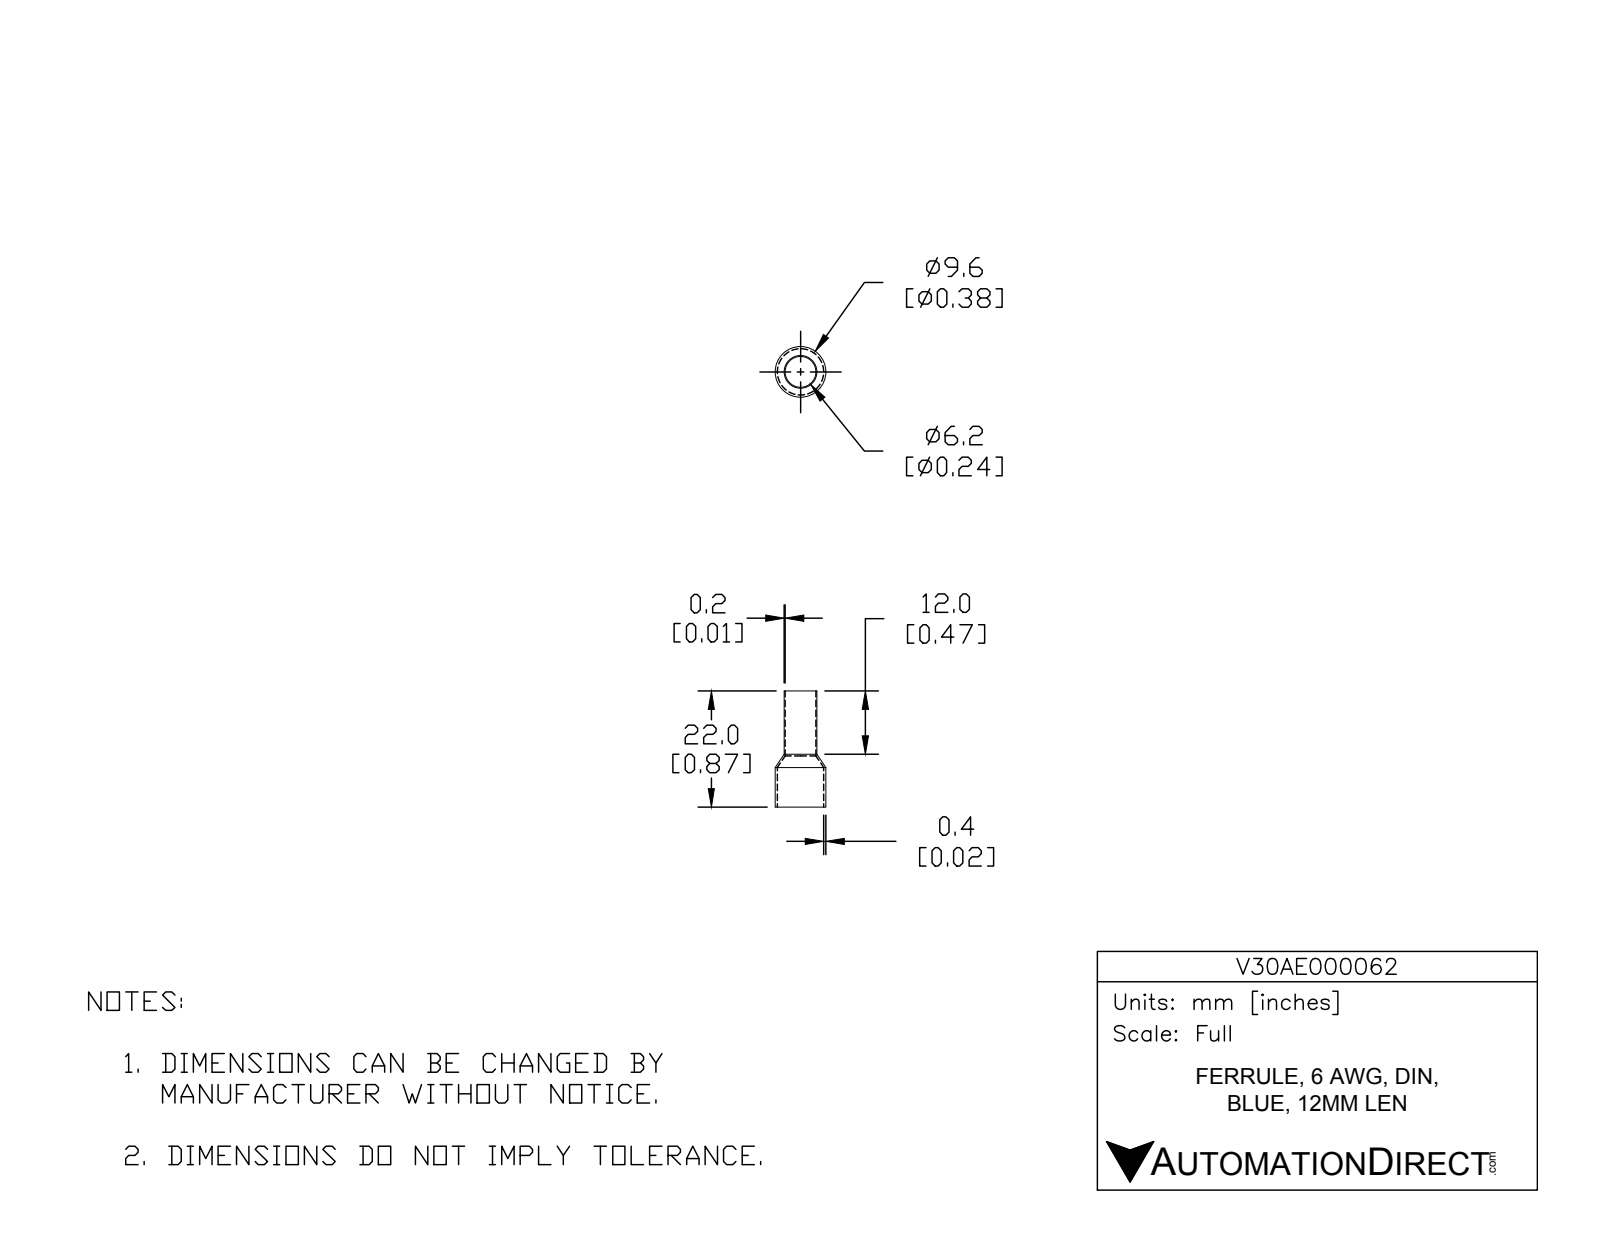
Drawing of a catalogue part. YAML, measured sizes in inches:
part_name: "V30AE000062"
step_written_by: "SolidWorks 2017 (AUTOMOTIVE_DESIGN)"
units: inches
bodies: {solids: 1, faces: 14, planar: 2, cylindrical: 8, other: 4}
overall_size: [0.866, 0.378, 0.378]
volume: 0.009
surface_area: 1.617
round_holes:
  - {diameter: 0.228, count: 1}
  - {diameter: 0.346, count: 1}
round_bosses_or_shafts:
  - {diameter: 0.378, count: 1}
  - {diameter: 0.244, count: 1}
face_to_face_distances: [0.866]
